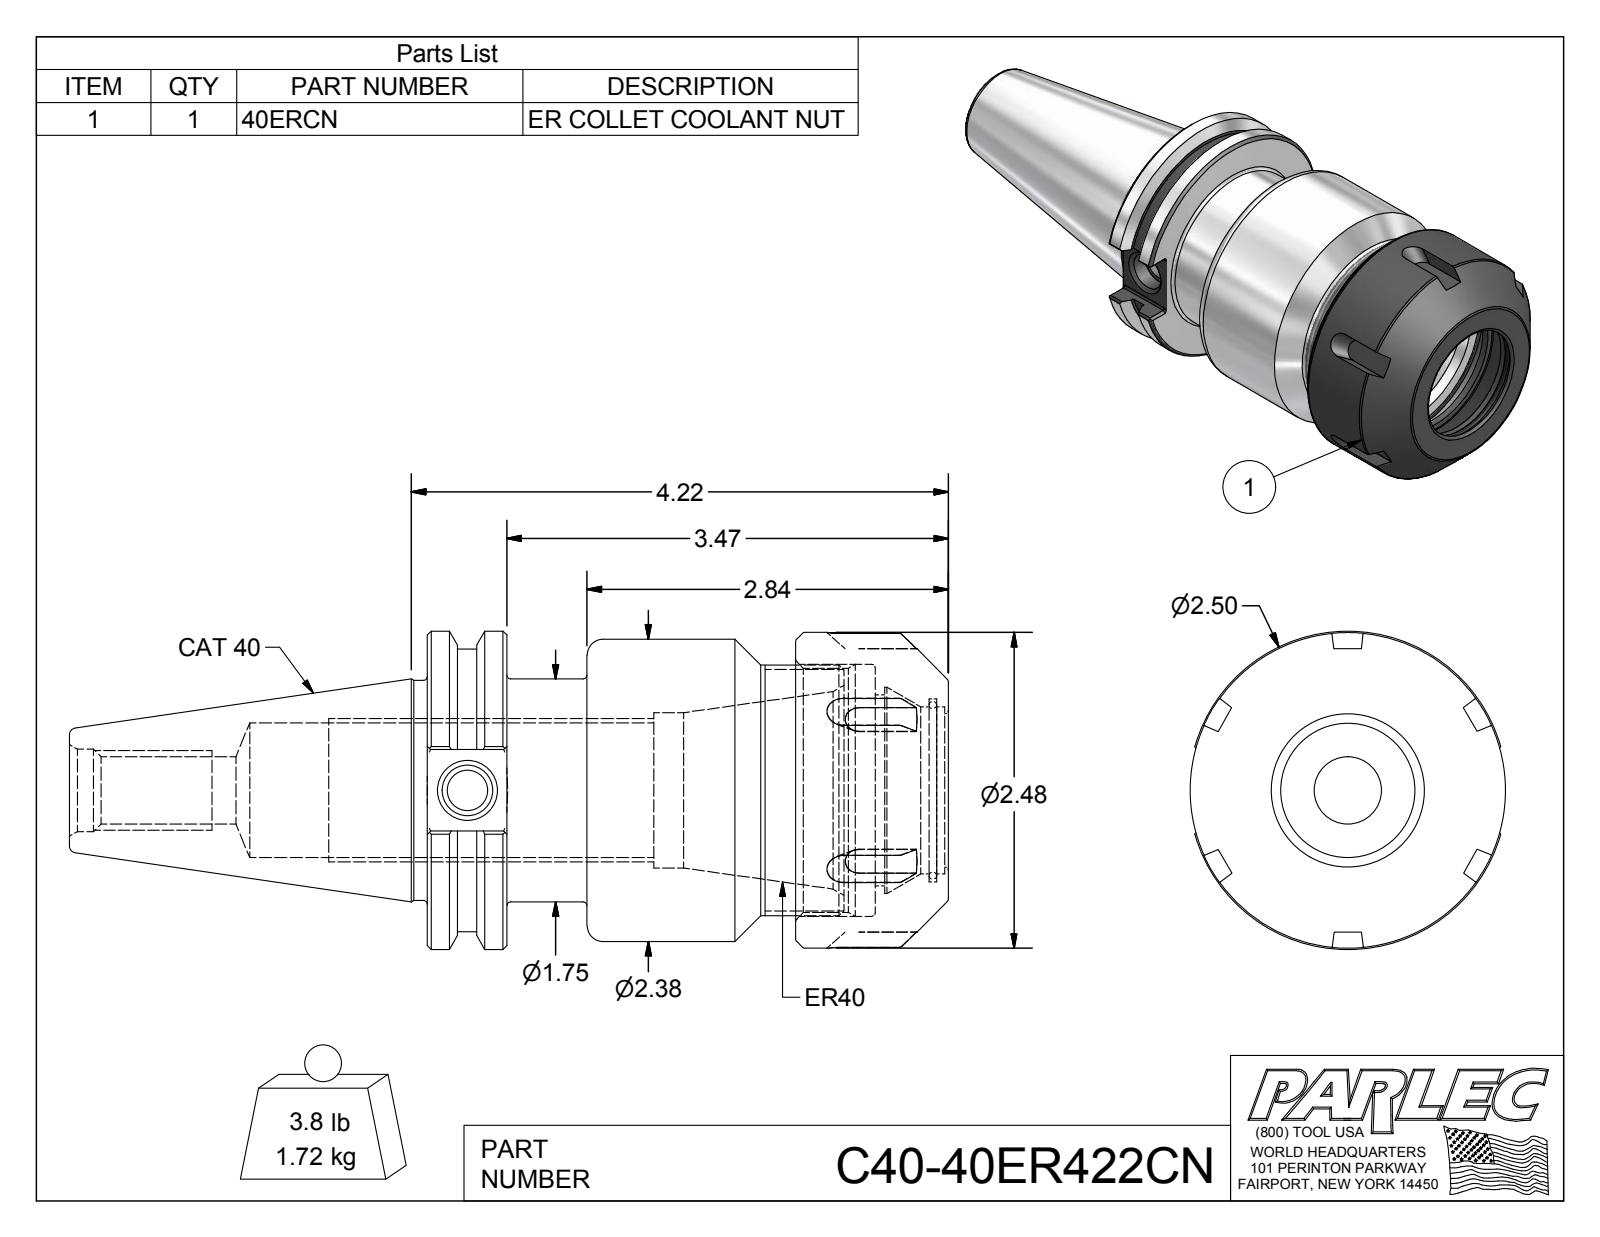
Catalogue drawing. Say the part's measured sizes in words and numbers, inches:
The part is named "C40-40ER422CN; C40-40ER4-1; 40ERCN". Its 3-D file was written by "Autodesk Inventor 2012 (AUTOMOTIVE_DESIGN)". It is 2 solids with 143 faces: 59 planar, 36 cylindrical and 48 other. Overall it measures 6.908 by 2.5 by 2.479 inches. Its volume is 13.34 cubic inches and its surface area 86.87 square inches. Round holes: 1 of diameter 0.315, 1 of diameter 0.399, 1 of diameter 0.527, 1 of diameter 0.648, 1 of diameter 1.057, 1 of diameter 1.22, 1 of diameter 1.313, 1 of diameter 1.437, 1 of diameter 1.5, 1 of diameter 1.62, 1 of diameter 1.916, 1 of diameter 1.98. Round bosses or shafts: 1 of diameter 2.5, 1 of diameter 2.48, 1 of diameter 2.375, 1 of diameter 2.219, 1 of diameter 1.969, 1 of diameter 1.75, 1 of diameter 1.73. Partial cylindrical surfaces (rounded edges, fillets, slot ends): 12 of radius 0.02. The main face-to-face distances are 0.625, 2.895, 3.52, 4.095, 3.47, 0.575, 1.255, 0.63, 2.265, 2.84.
